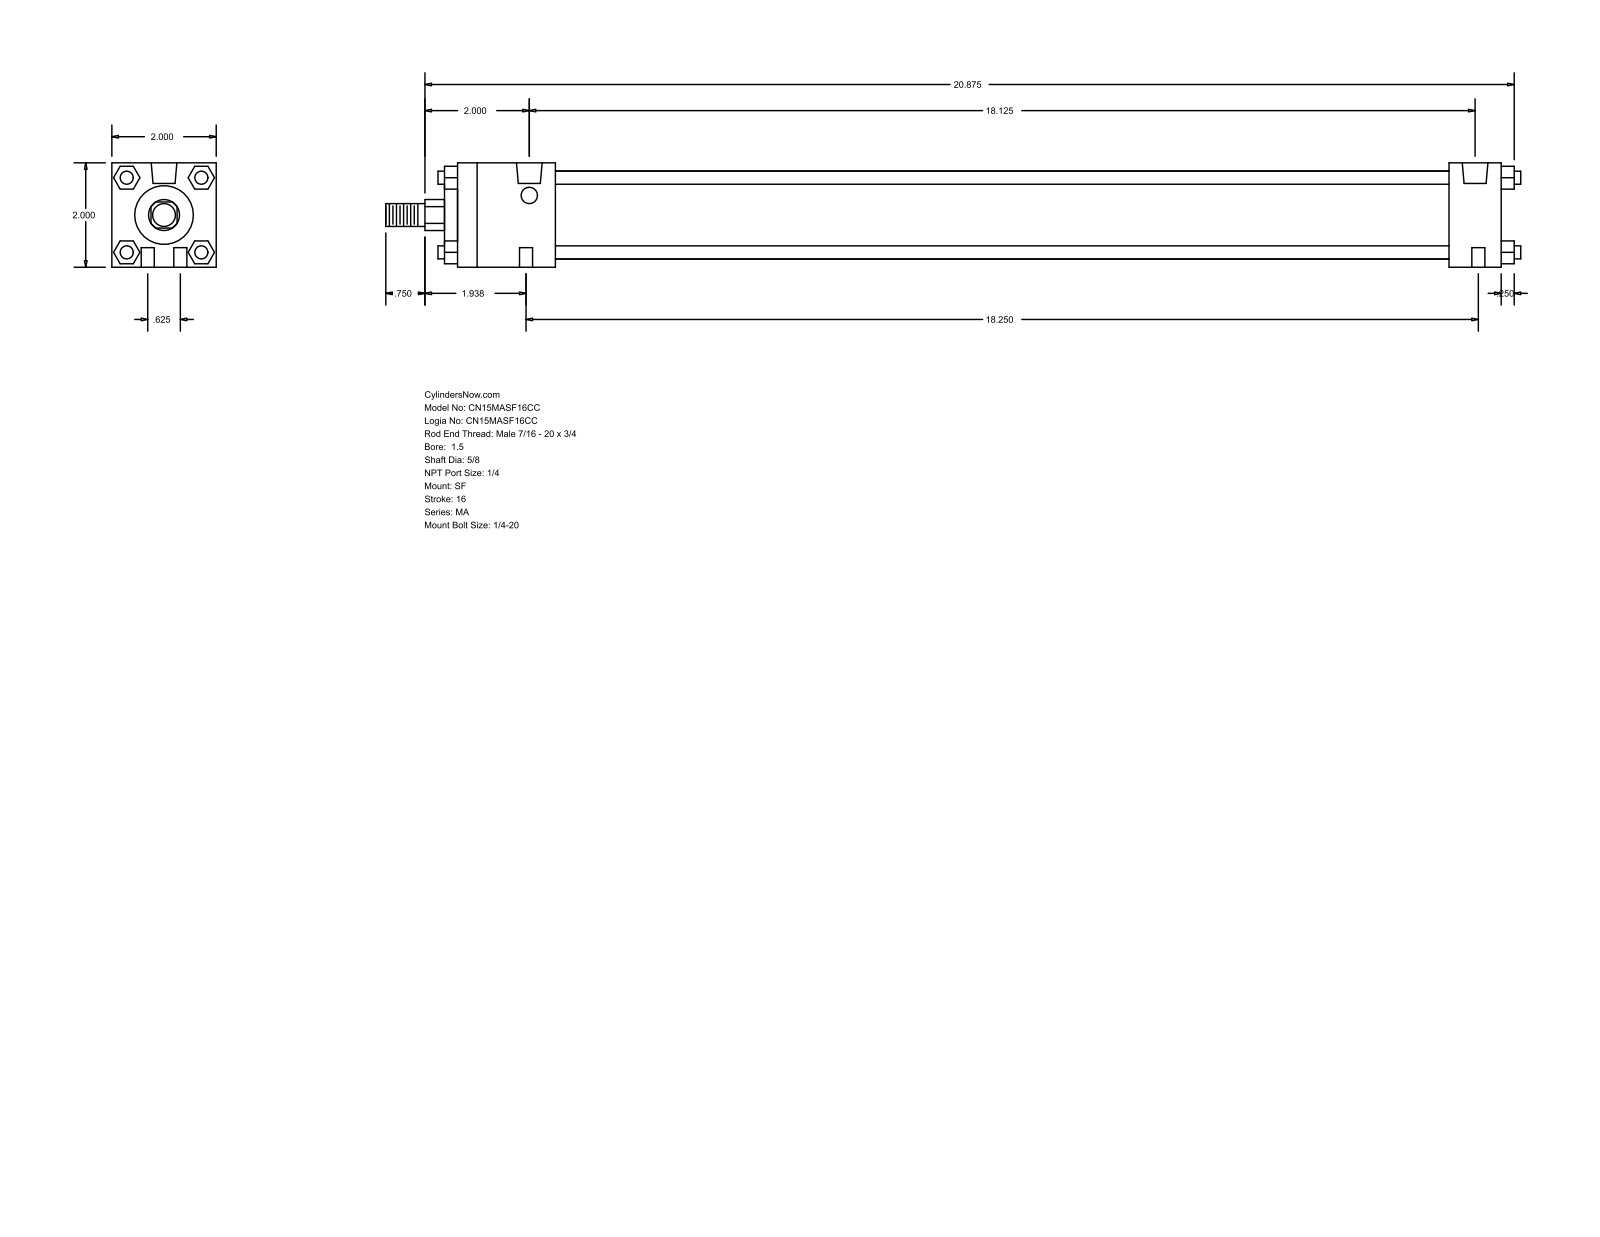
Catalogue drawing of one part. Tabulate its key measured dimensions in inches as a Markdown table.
| quantity | value |
| --- | --- |
| part name | MA_SF__0150_0.625 |
| STEP written by | GSSL Pune (CONFIG_CONTROL_DESIGN) |
| units | inches |
| bodies | 0 solids, 124 faces (94 planar, 30 cylindrical, 0 other) |
| overall size | 21.75 × 2 × 2 |
| round holes (diameter × count) | 0.25 × 4, 0.313 × 2, 0.492 × 2 |
| round bosses / shafts (diameter × count) | 0.25 × 4, 1.69 × 1, 1.125 × 1, 0.625 × 1, 0.437 × 1 |
| partial cylindrical surfaces (radius × count) | 0.297 × 1 |
| main face-to-face distances | 2, 20, 0.25, 1, 20.25, 1.875, 19, 17.125, 18.125, 2.125 |
| hole center spacings | 0.319, 0.625, 18.125, 18.19, 18.191, 18.25, 18.261 |
